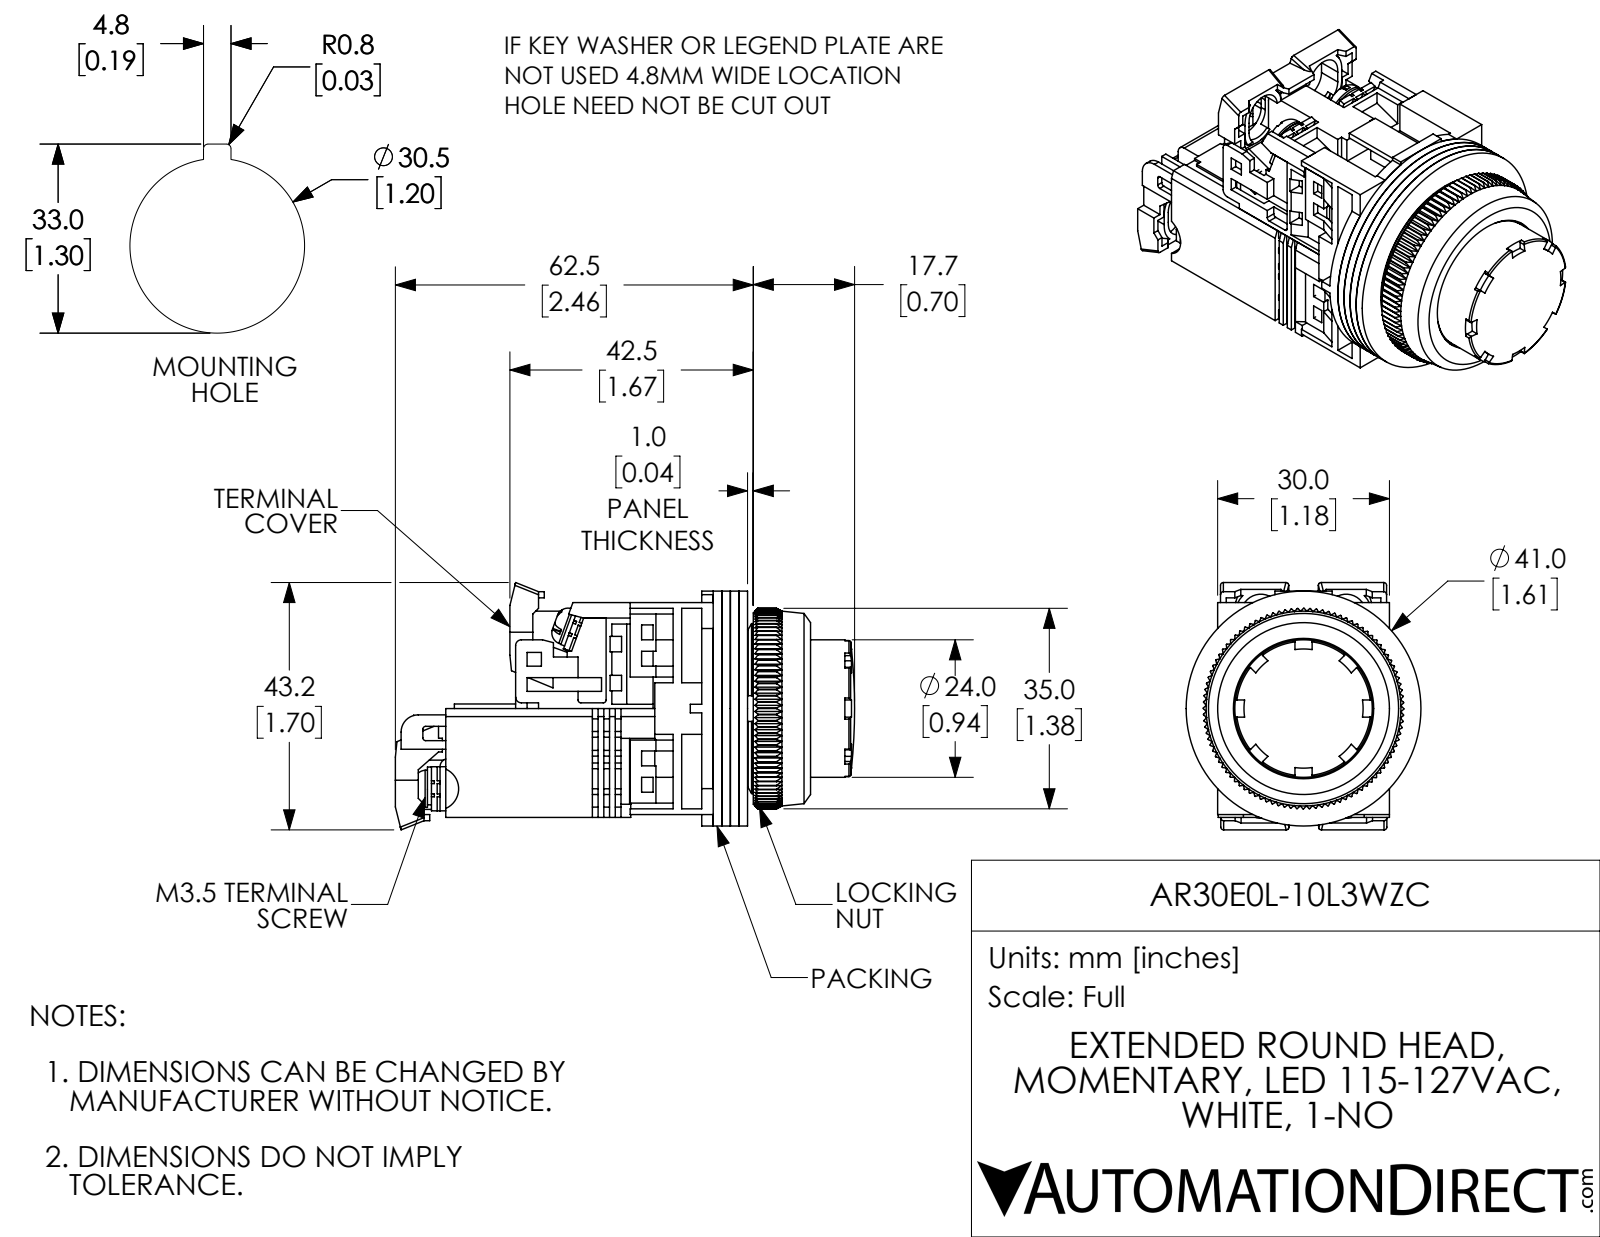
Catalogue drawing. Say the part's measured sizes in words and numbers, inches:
The part is named "AR30E0L-10L3WZC". Its 3-D file was written by "SolidWorks 2017 (AUTOMOTIVE_DESIGN)". It is 27 solids with 1960 faces: 1368 planar, 339 cylindrical and 253 other. Overall it measures 3.157 by 1.7 by 1.614 inches. Its volume is 2.883 cubic inches and its surface area 64.03 square inches. Round holes: 6 of diameter 0.138, 4 of diameter 0.142, 3 of diameter 0.118, 1 of diameter 0.472, 1 of diameter 0.709, 1 of diameter 0.728, 1 of diameter 0.787, 1 of diameter 0.945, 1 of diameter 0.965, 1 of diameter 1.122, 1 of diameter 1.252. Round bosses or shafts: 4 of diameter 0.26, 2 of diameter 0.138, 1 of diameter 1.614, 1 of diameter 1.181, 1 of diameter 0.866, 1 of diameter 0.776, 1 of diameter 0.551. Partial cylindrical surfaces (rounded edges, fillets, slot ends): 17 of radius 0.059, 16 of radius 0.012, 13 of radius 0.02, 4 of radius 0.138, 4 of radius 0.177, 2 of radius 0.039, 2 of radius 0.118, 1 of radius 0.016. The main face-to-face distances are 0.059, 0.118, 0.177, 0.748, 0.039, 0.02, 0.079, 1.417, 0.689, 0.047. The hole center spacings are 0.579, 0.02, 0.295, 0.299, 0.3, 0.583, 0.583, 0.605.
